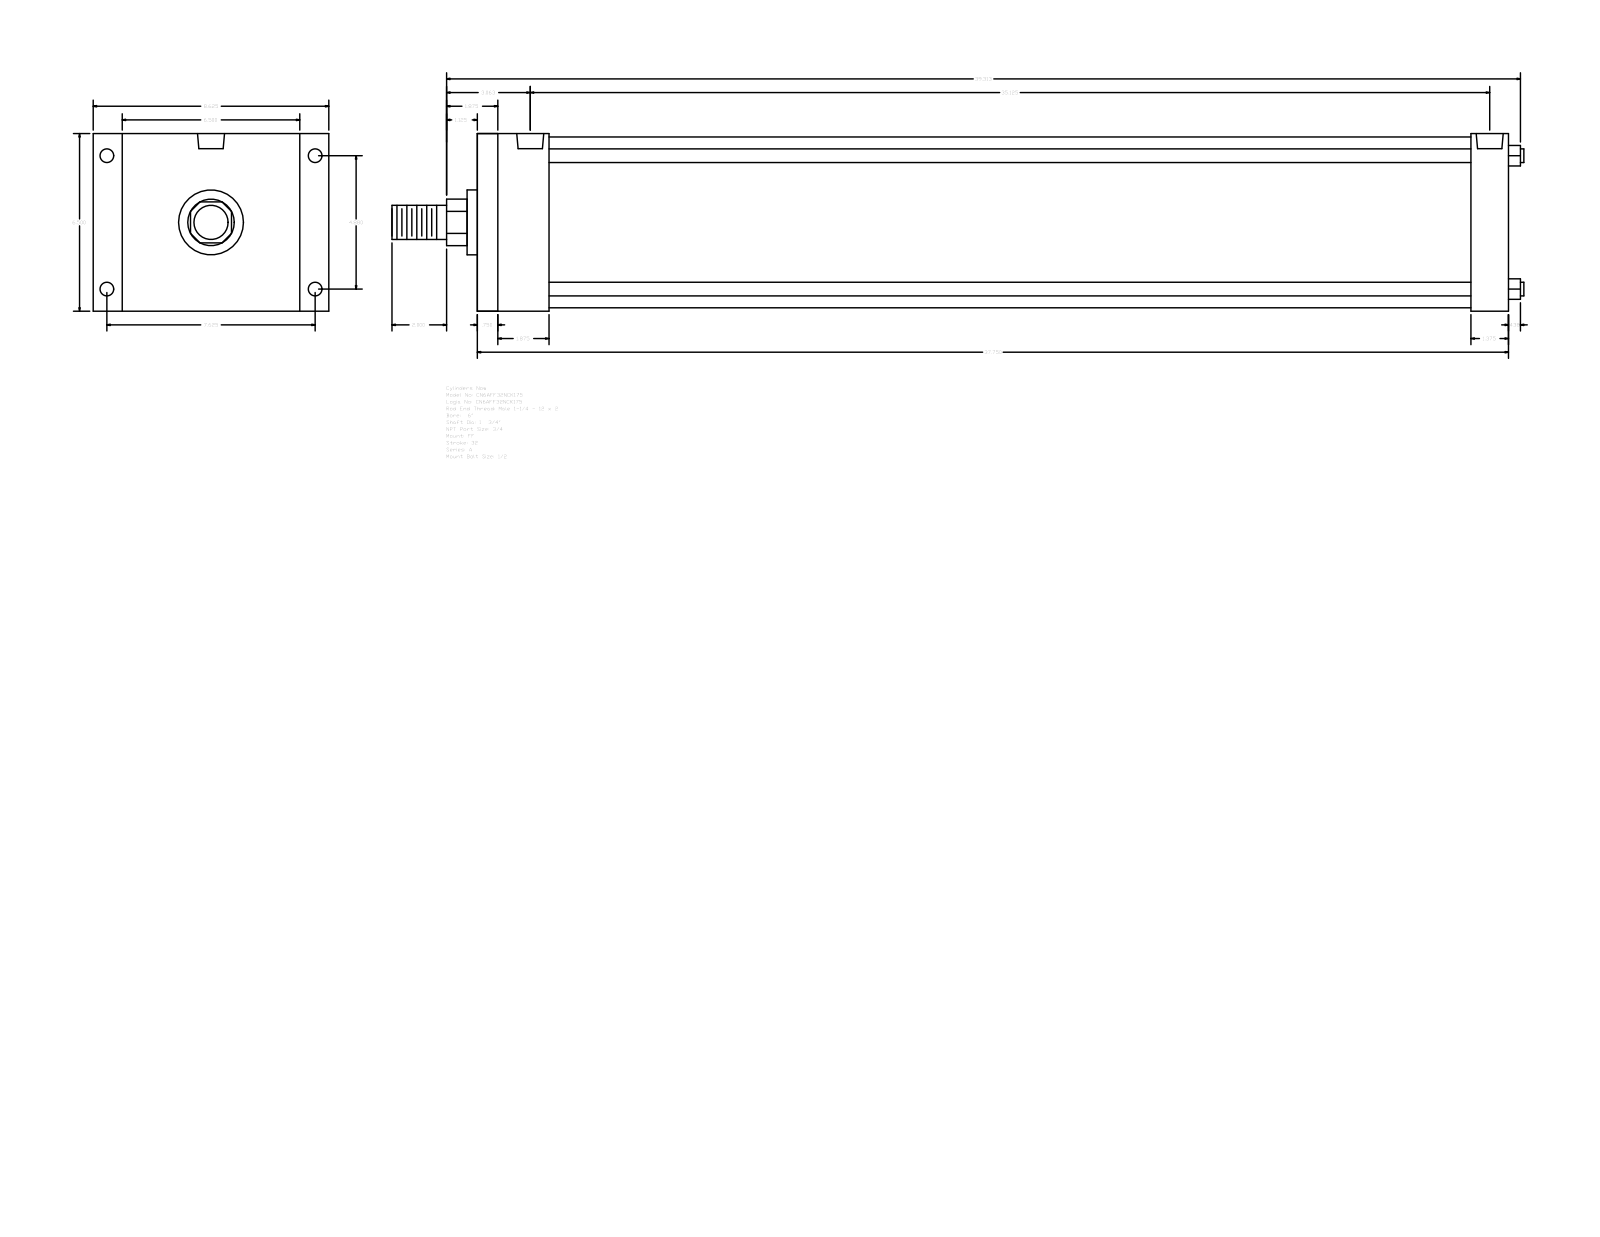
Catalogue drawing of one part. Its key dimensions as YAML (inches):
part_name: "A_FF__0600_1.75"
step_written_by: "GSSL Pune (CONFIG_CONTROL_DESIGN)"
units: inches
bodies: {solids: 0, faces: 92, planar: 64, cylindrical: 28, other: 0}
overall_size: [41.437, 8.625, 6.5]
round_holes:
  - {diameter: 0.5, count: 4}
  - {diameter: 0.594, count: 4}
  - {diameter: 0.989, count: 2}
round_bosses_or_shafts:
  - {diameter: 0.5, count: 4}
  - {diameter: 6.25, count: 1}
  - {diameter: 2.375, count: 1}
  - {diameter: 1.75, count: 1}
  - {diameter: 1.25, count: 1}
partial_cylinders:
  - {radius: 0.852, count: 1}
face_to_face_distances: [6.5, 37.75, 0.75, 37, 2.625, 1.875, 35.125, 36.375, 35.625, 33.75]
hole_center_spacings: [0.219, 4.88, 7.625, 9.053, 34.687, 34.906, 35.125]
